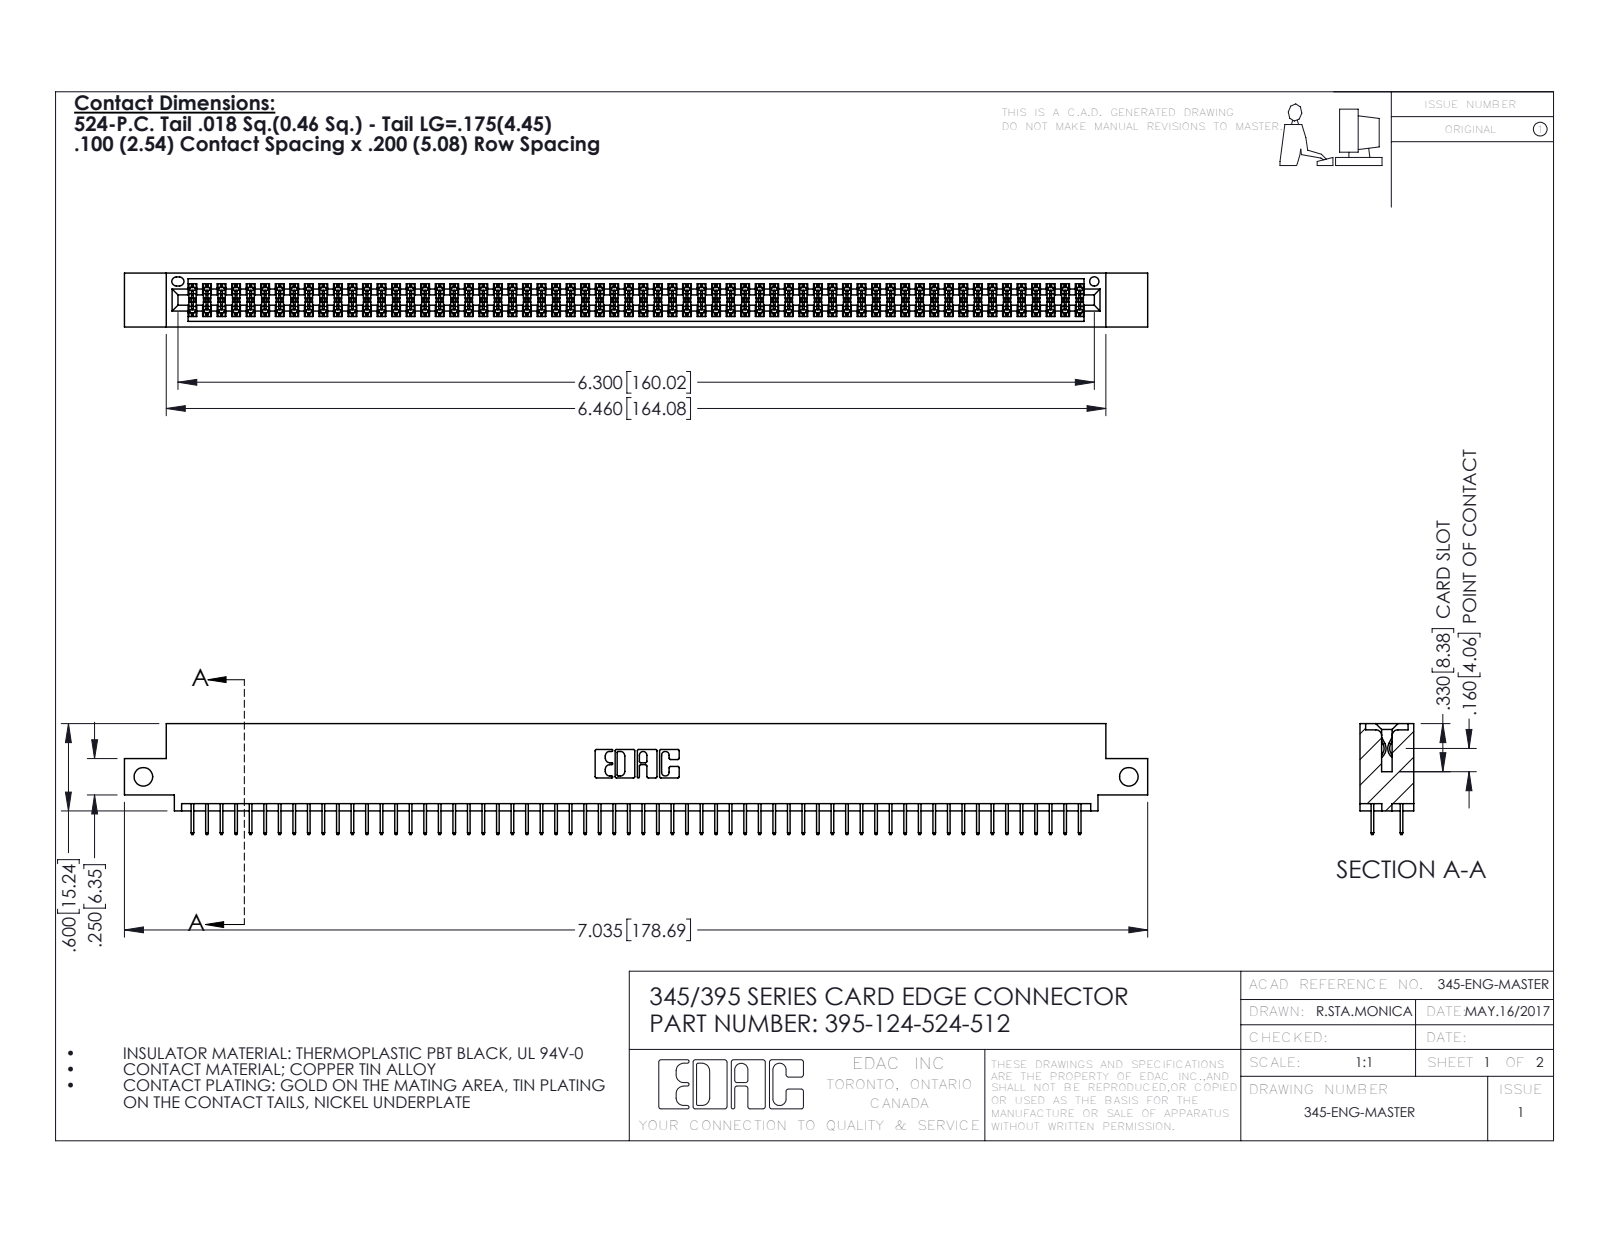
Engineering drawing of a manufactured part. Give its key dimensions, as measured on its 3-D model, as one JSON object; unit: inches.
{"part_name": "395-124-524-512; 345 Part_0.110 Offset - Side Mount; 345-292-001_345-293-124", "step_written_by": "SolidWorks 2016 (CONFIG_CONTROL_DESIGN)", "units": "inches", "bodies": {"solids": 125, "faces": 6826, "planar": 4920, "cylindrical": 1906, "other": 0}, "overall_size": [7.035, 0.762, 0.37], "volume_in3": 1.049, "surface_area_in2": 39.16, "round_holes": [[0.128, 2], [0.064, 1]], "partial_cylinders_radius": [[0.006, 186], [0.01, 22], [0.007, 6], [0.031, 6], [0.026, 3], [0.014, 2], [0.019, 2], [0.022, 2]], "face_to_face_distances": [0.072, 0.298, 0.2, 0.37, 0.098, 0.272, 0.025, 0.225, 0.072, 0.175], "hole_center_spacings": [6.775]}
